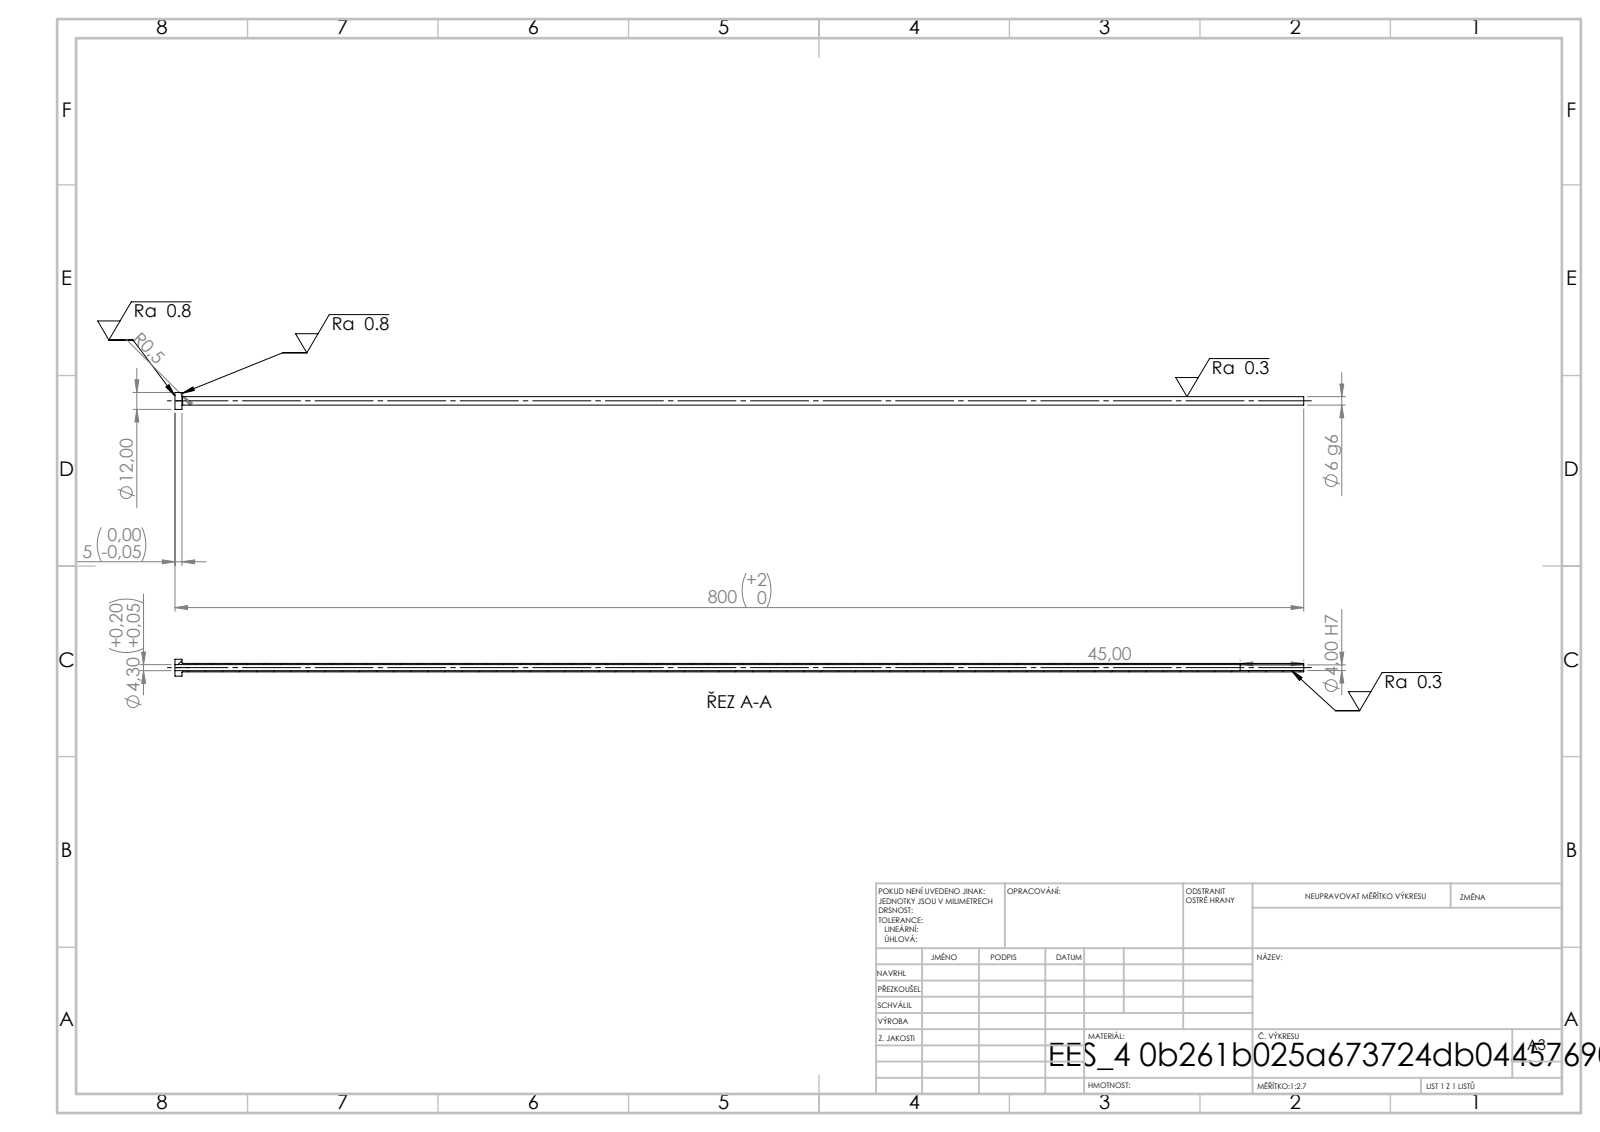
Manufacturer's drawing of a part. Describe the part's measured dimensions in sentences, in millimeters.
Its 3-D file was written by "SolidWorks 2019 (CONFIG_CONTROL_DESIGN)". It is 1 solid with 14 faces: 4 planar, 8 cylindrical and 2 other. Overall it measures 800 by 12 by 12 millimeters. Its volume is 11 515 cubic millimeters and its surface area 26 136 square millimeters. Round holes: 1 of diameter 4, 1 of diameter 4.3. Round bosses or shafts: 1 of diameter 12, 1 of diameter 6. The main face-to-face distances are 5, 800, 795, 755, 750, 45.
